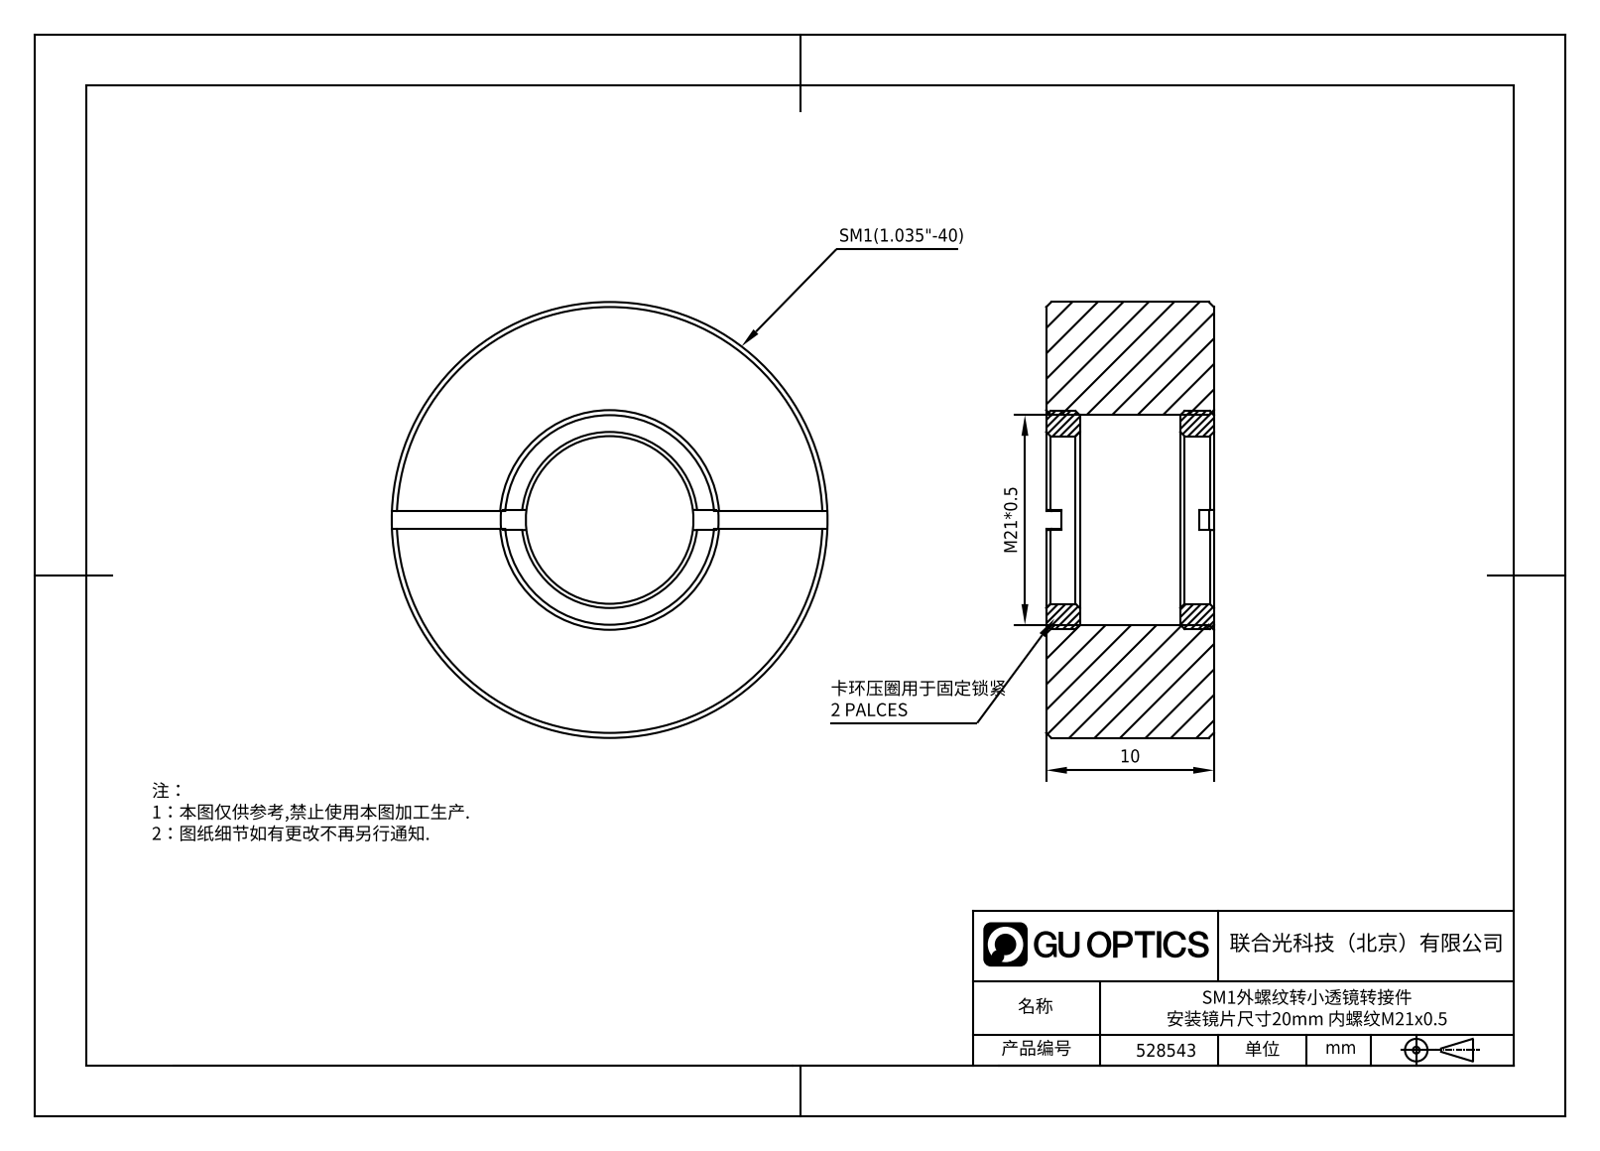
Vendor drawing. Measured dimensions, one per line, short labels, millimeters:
name: 528543
written by: SolidWorks 2020 (CONFIG_CONTROL_DESIGN)
unit: mm
bodies: 3 solids, 51 faces (27 planar, 6 cylindrical, 18 other)
size: 26 × 26 × 10
volume: 2 336 mm³; area: 2 607 mm²
holes: 1× ⌀18, 1× ⌀20.5
bosses: 1× ⌀26, 1× ⌀21
face distances: 10, 2, 8, 6, 1.1, 1, 1.15, 0.9, 9.1, 7.1
